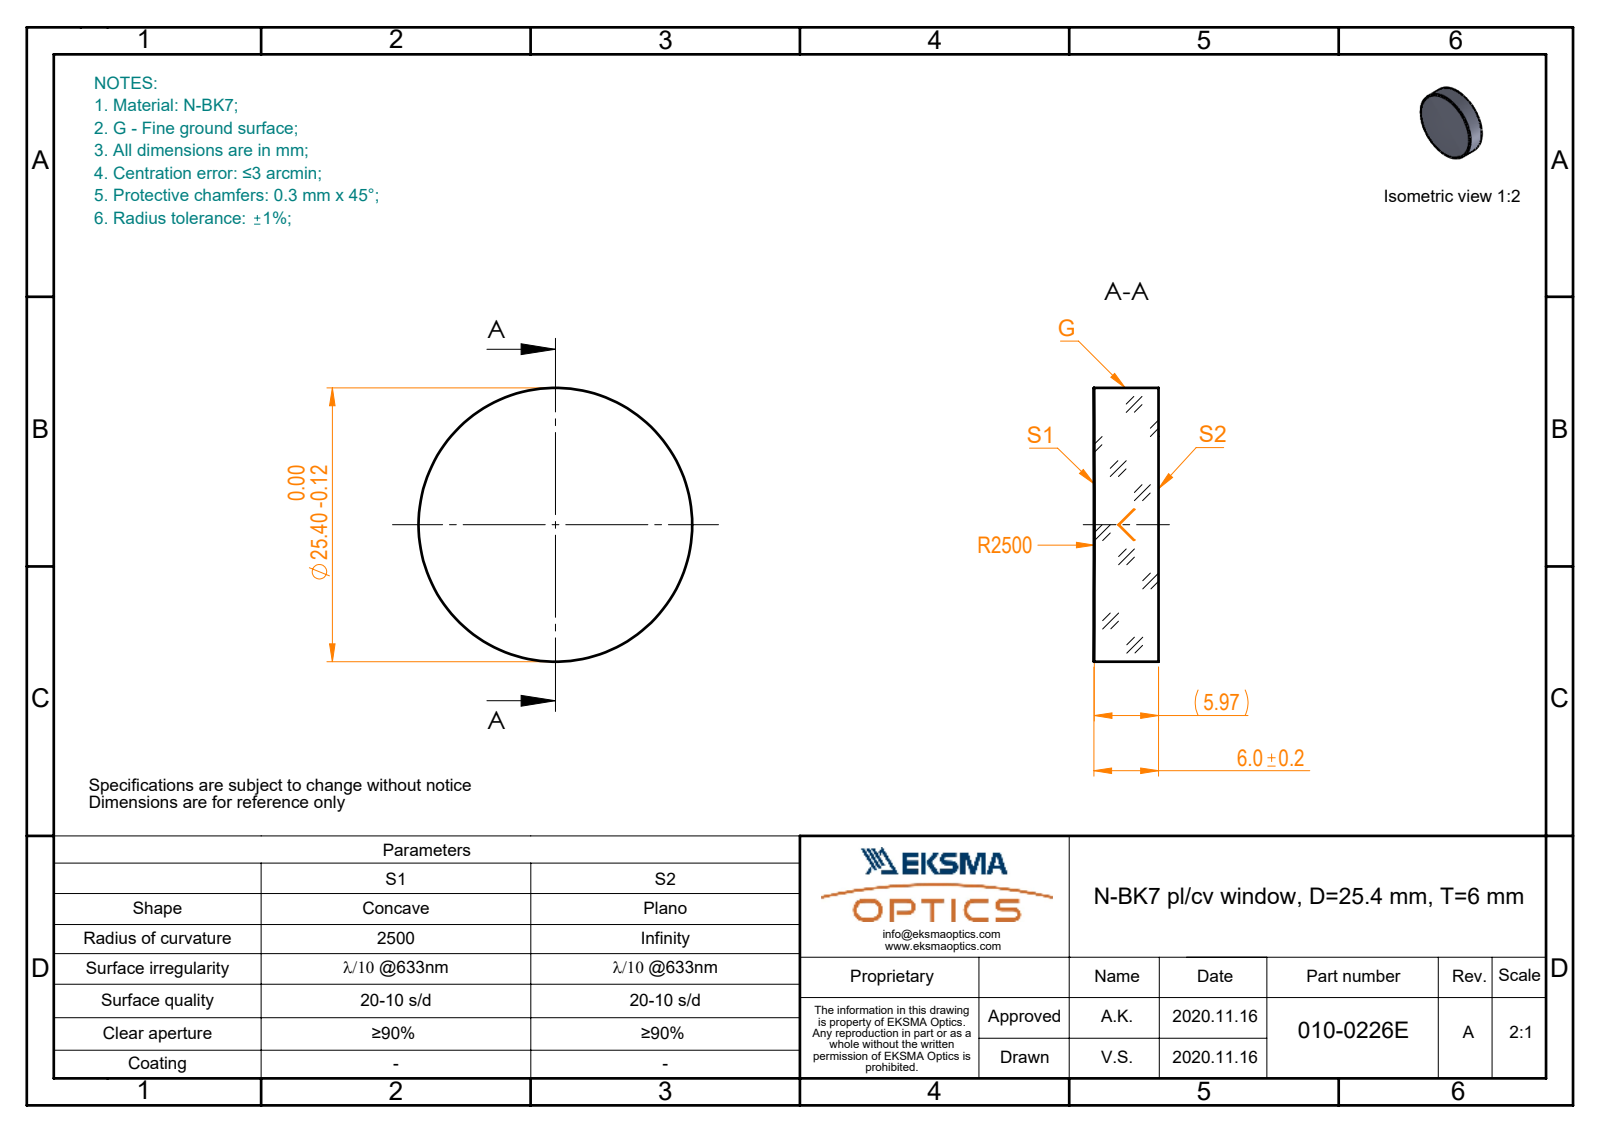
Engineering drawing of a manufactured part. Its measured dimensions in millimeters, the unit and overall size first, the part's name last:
Units: millimetres
Overall size (bounding box): 25.4 × 25.4 × 6
Round bosses / shafts (diameter × count): ⌀25.4 ×1
Volume: 3 032 mm³ · Surface area: 1 492 mm²
Bodies: 1 solid, 5 faces (1 planar, 2 cylindrical, 2 other)
Part name (STEP PRODUCT): 010-0226E_N-BK7_PCV_window
STEP written by: SolidWorks 2019 (CONFIG_CONTROL_DESIGN)
